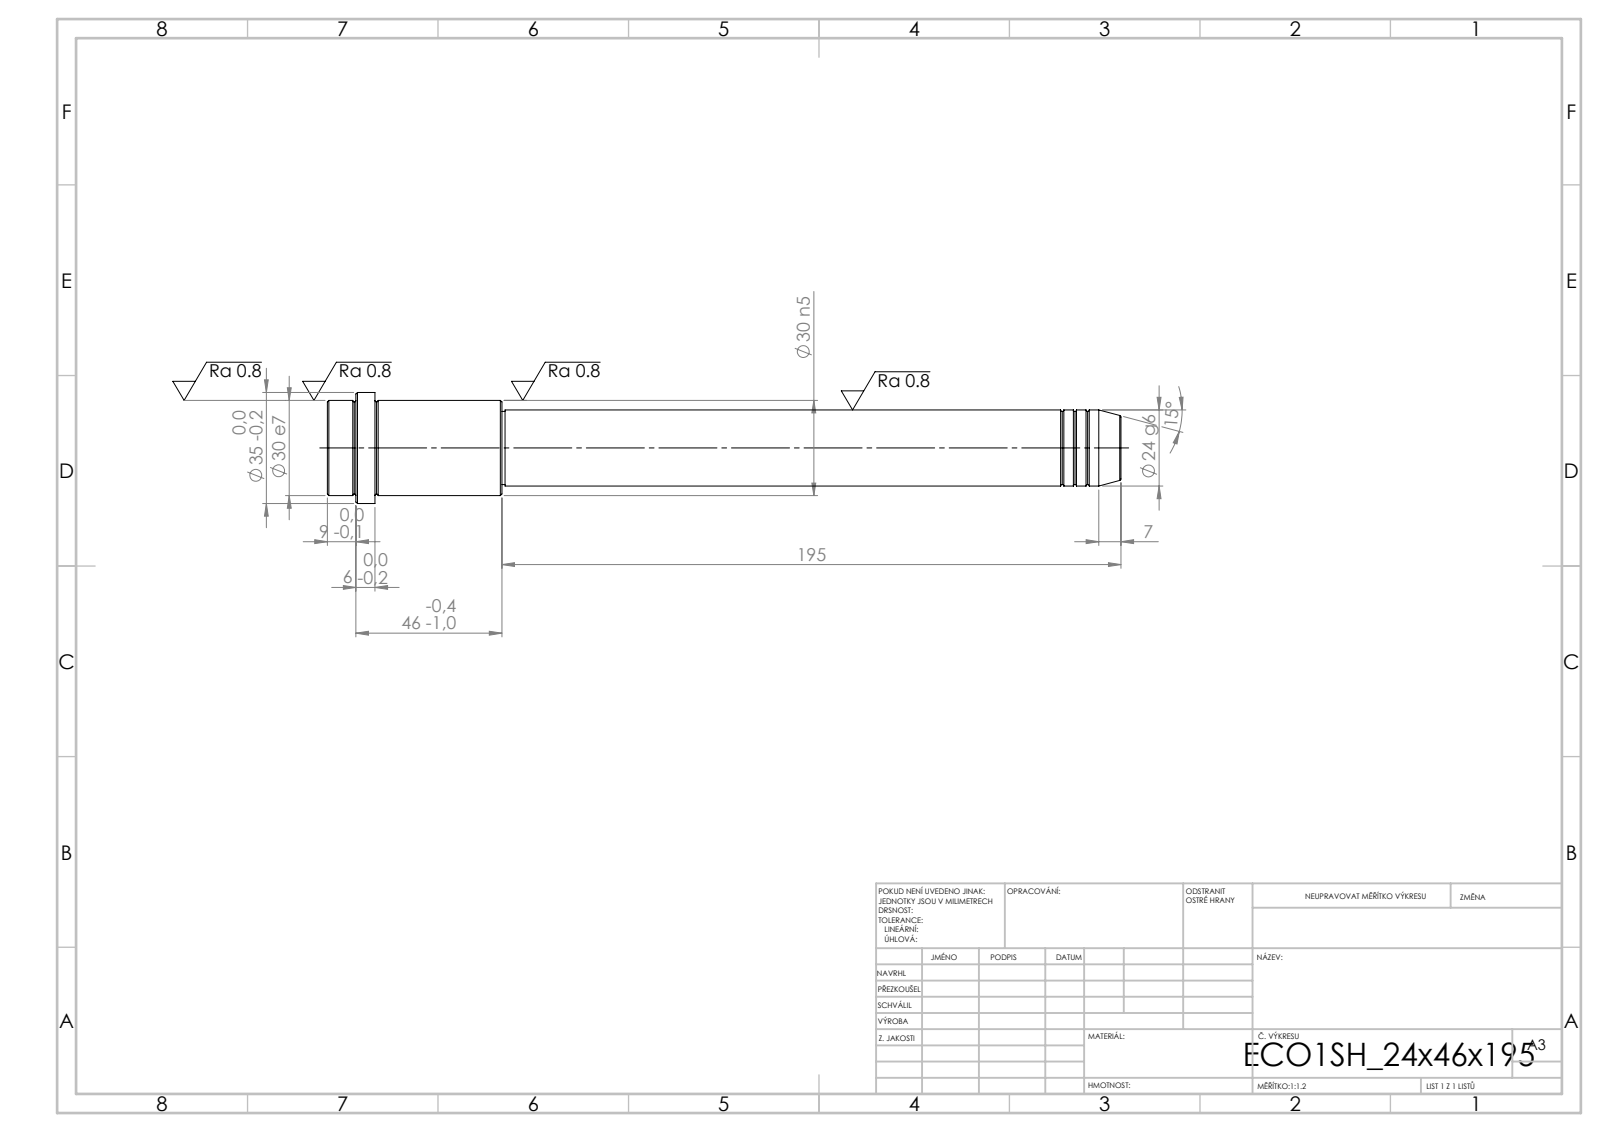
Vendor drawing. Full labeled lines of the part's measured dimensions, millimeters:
STEP written by: SolidWorks 2019 (CONFIG_CONTROL_DESIGN)
Units: millimetres
Bodies: 1 solid, 52 faces (6 planar, 16 cylindrical, 30 other)
Overall size (bounding box): 250 × 35 × 35
Volume: 127 920 mm³ · Surface area: 21 946 mm²
Round bosses / shafts (diameter × count): ⌀35 ×1, ⌀30 ×1, ⌀24 ×1, ⌀23 ×1
Main face-to-face distances: 250, 235, 15, 195, 40, 55, 241, 46, 6, 9
